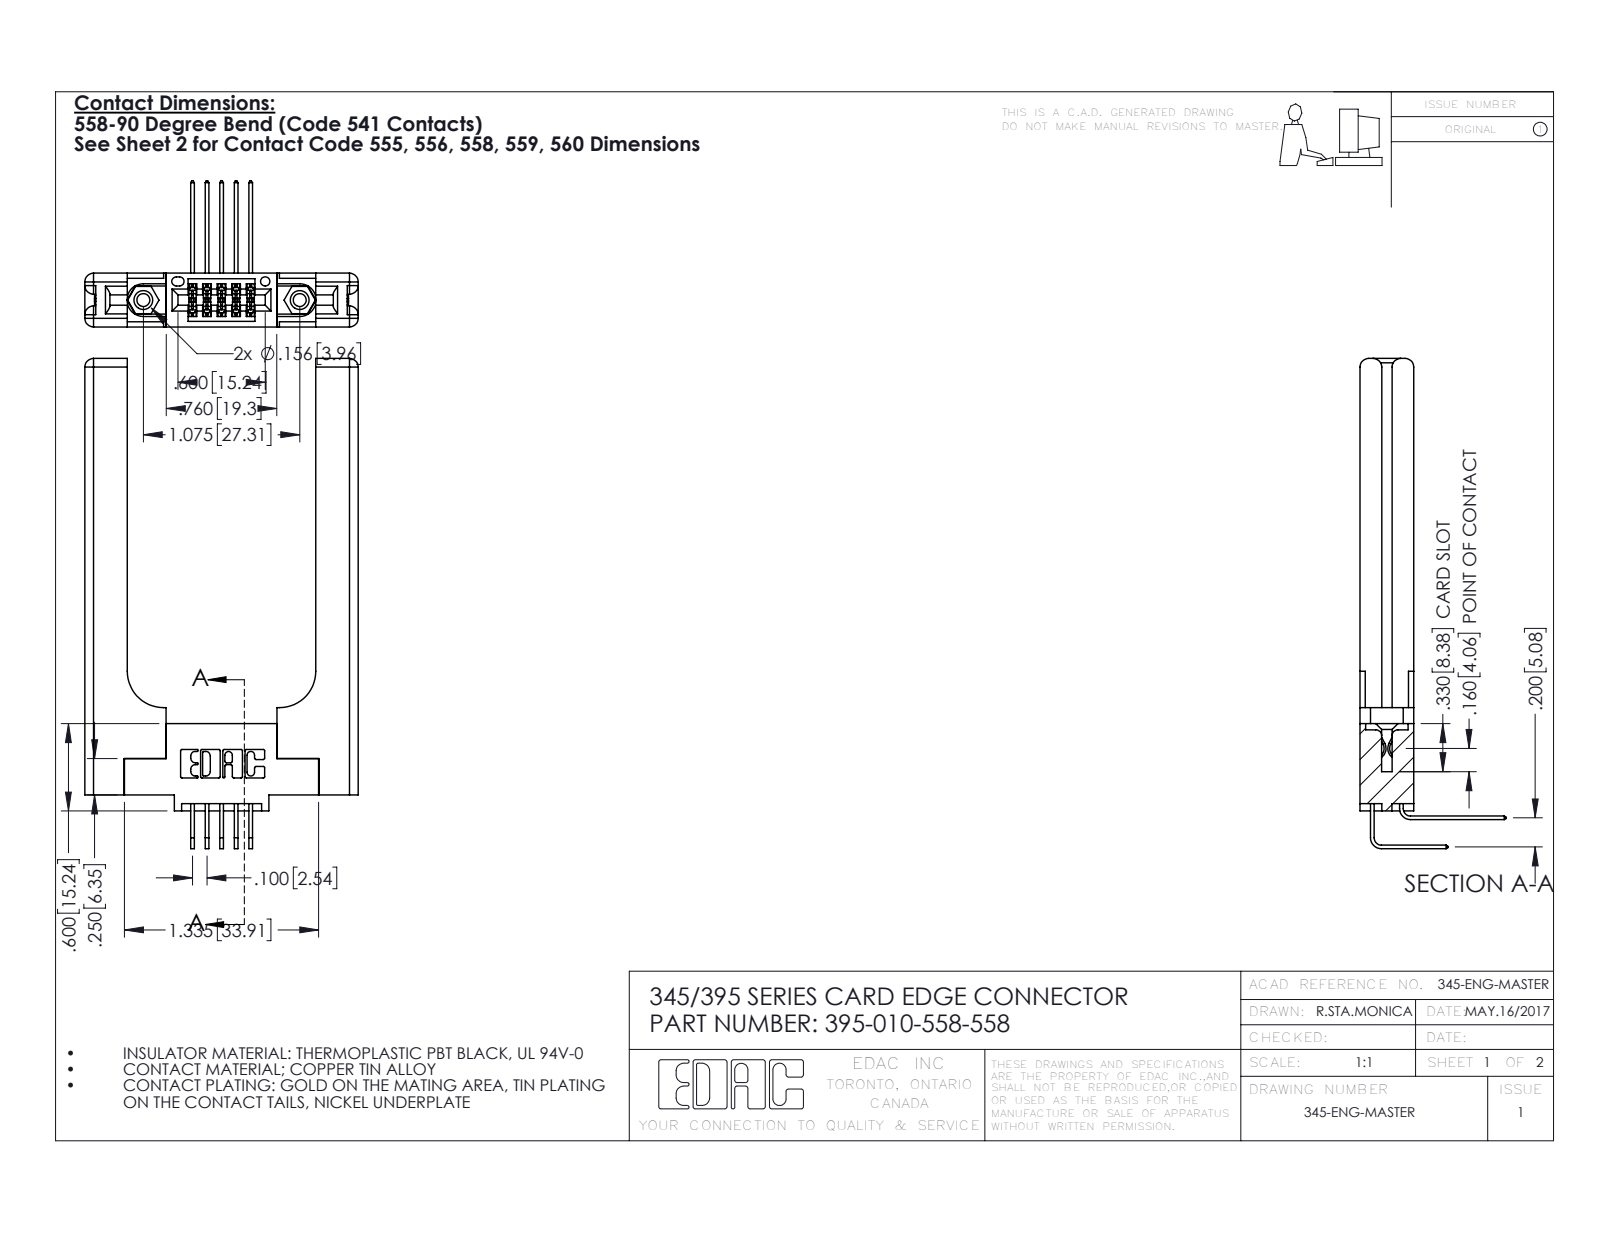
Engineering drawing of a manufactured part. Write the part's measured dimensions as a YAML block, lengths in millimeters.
part_name: "345 Part_0.110 Offset - 0.156 Dia-TH; 345-292-001_558 559 Tail - 1; 345-220-058_345-220-058; 395-010-558-558 (+2 more)"
step_written_by: "SolidWorks 2016 (CONFIG_CONTROL_DESIGN)"
units: millimeters
bodies: {solids: 15, faces: 906, planar: 582, cylindrical: 264, other: 60}
overall_size: [85.6, 47.7, 25.5]
volume: 12700
surface_area: 11030
round_holes:
  - {diameter: 2.3, count: 2}
  - {diameter: 3.2, count: 2}
  - {diameter: 4, count: 2}
  - {diameter: 1.6, count: 1}
round_bosses_or_shafts:
  - {diameter: 3.9, count: 2}
partial_cylinders:
  - {radius: 0.3, count: 22}
  - {radius: 0.2, count: 16}
  - {radius: 1.5, count: 16}
  - {radius: 0.2, count: 6}
  - {radius: 0.8, count: 6}
  - {radius: 0.7, count: 3}
  - {radius: 0.4, count: 2}
  - {radius: 0.5, count: 2}
face_to_face_distances: [9.4, 3.8, 5.6, 1.8, 32.9, 3.8, 2, 7.6, 1.8, 7.4]
hole_center_spacings: [6.9, 21.5, 27.3]
